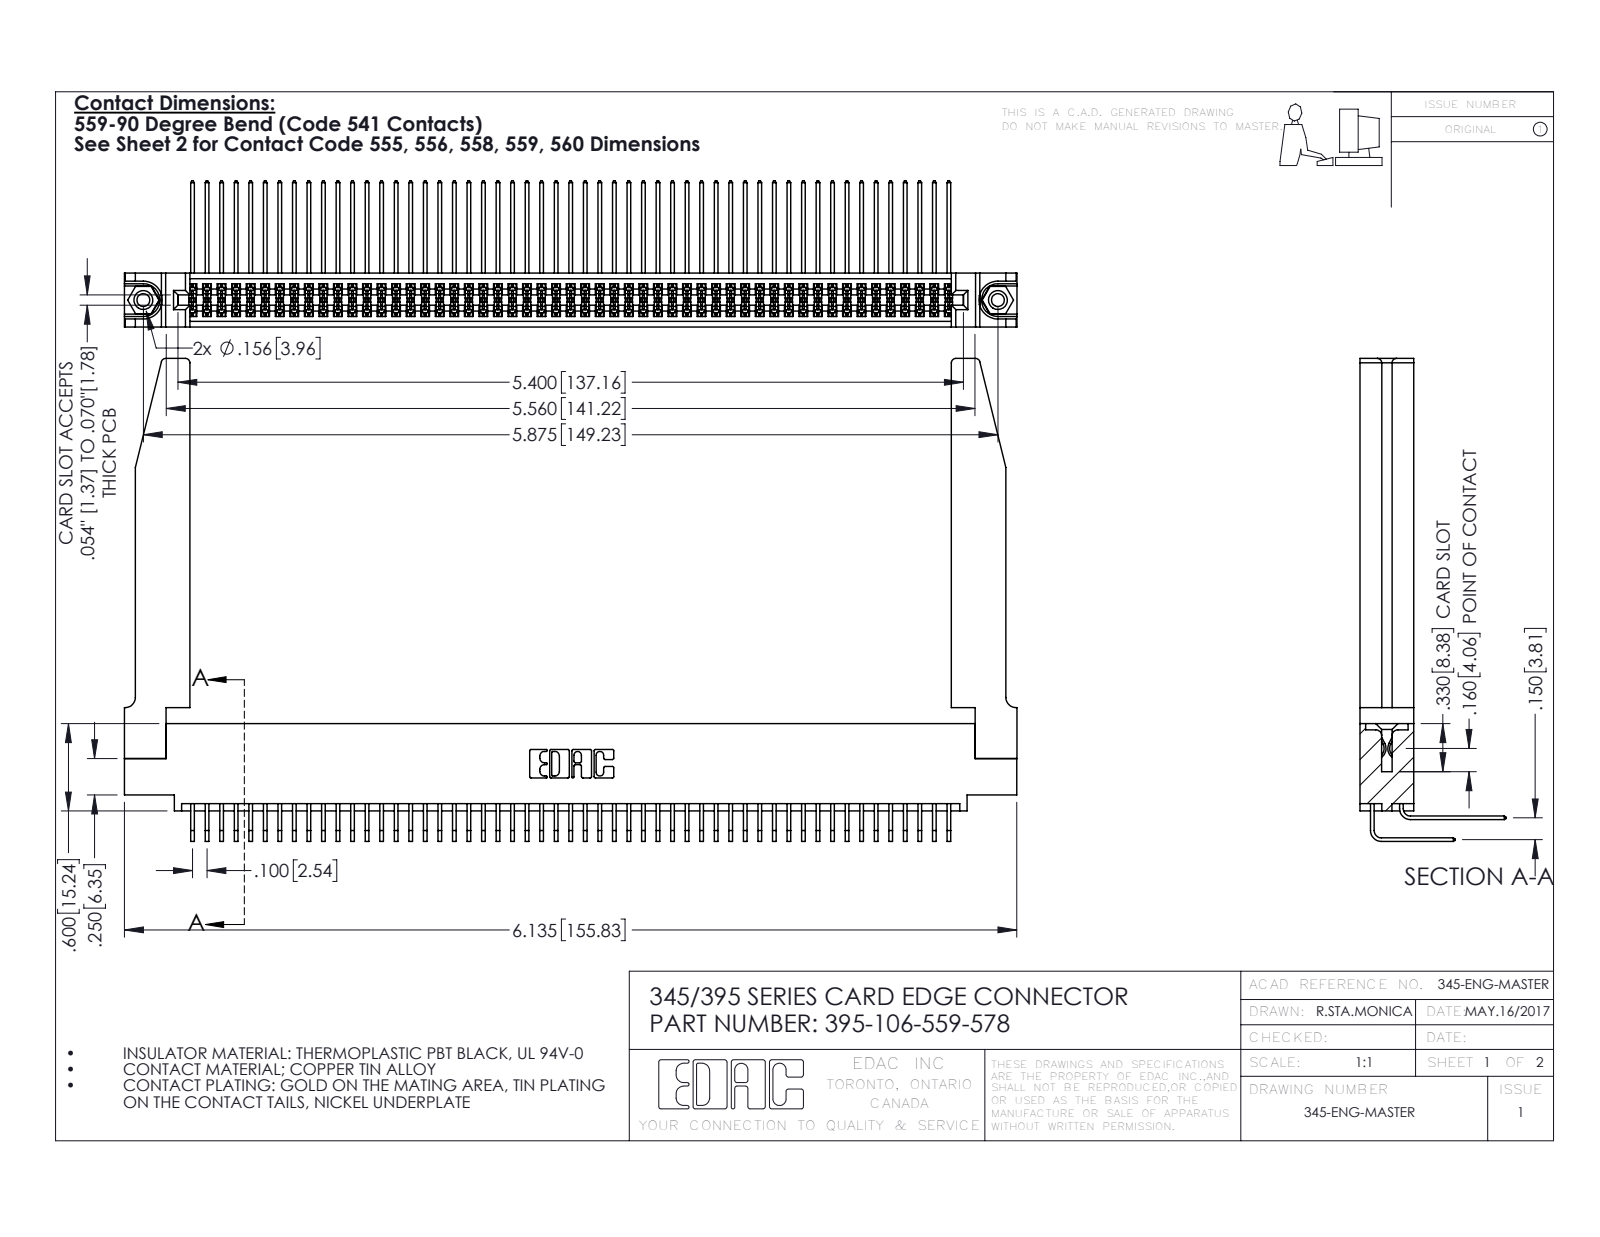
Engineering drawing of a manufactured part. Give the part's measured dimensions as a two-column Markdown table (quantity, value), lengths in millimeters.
| quantity | value |
| --- | --- |
| part name | 345-250-001_345-250-001-102; 345-292-001_559 Tail - 2; 345-292-001_558 559 Tail - 1; 345-220-078_345-220-078 (+2 more) |
| STEP written by | SolidWorks 2016 (CONFIG_CONTROL_DESIGN) |
| units | millimeters |
| bodies | 111 solids, 5876 faces (3936 planar, 1888 cylindrical, 52 other) |
| overall size | 155.9 × 84.3 × 25.5 |
| volume | 23 550 mm³ |
| surface area | 33 350 mm² |
| round holes (diameter × count) | 2.3 × 2, 3.2 × 2, 4 × 2, 1.6 × 1 |
| round bosses / shafts (diameter × count) | 3.9 × 2 |
| partial cylindrical surfaces (radius × count) | 0.2 × 159, 0.3 × 22, 0.8 × 8, 0.2 × 6, 0.8 × 6, 0.7 × 3, 0.4 × 2, 0.5 × 2 |
| main face-to-face distances | 1.8, 7.6, 9.4, 5.1, 2.5, 6.9, 0.6, 5.7, 4.4, 3.8 |
| hole center spacings | 6.9, 143.2, 149.2 |
